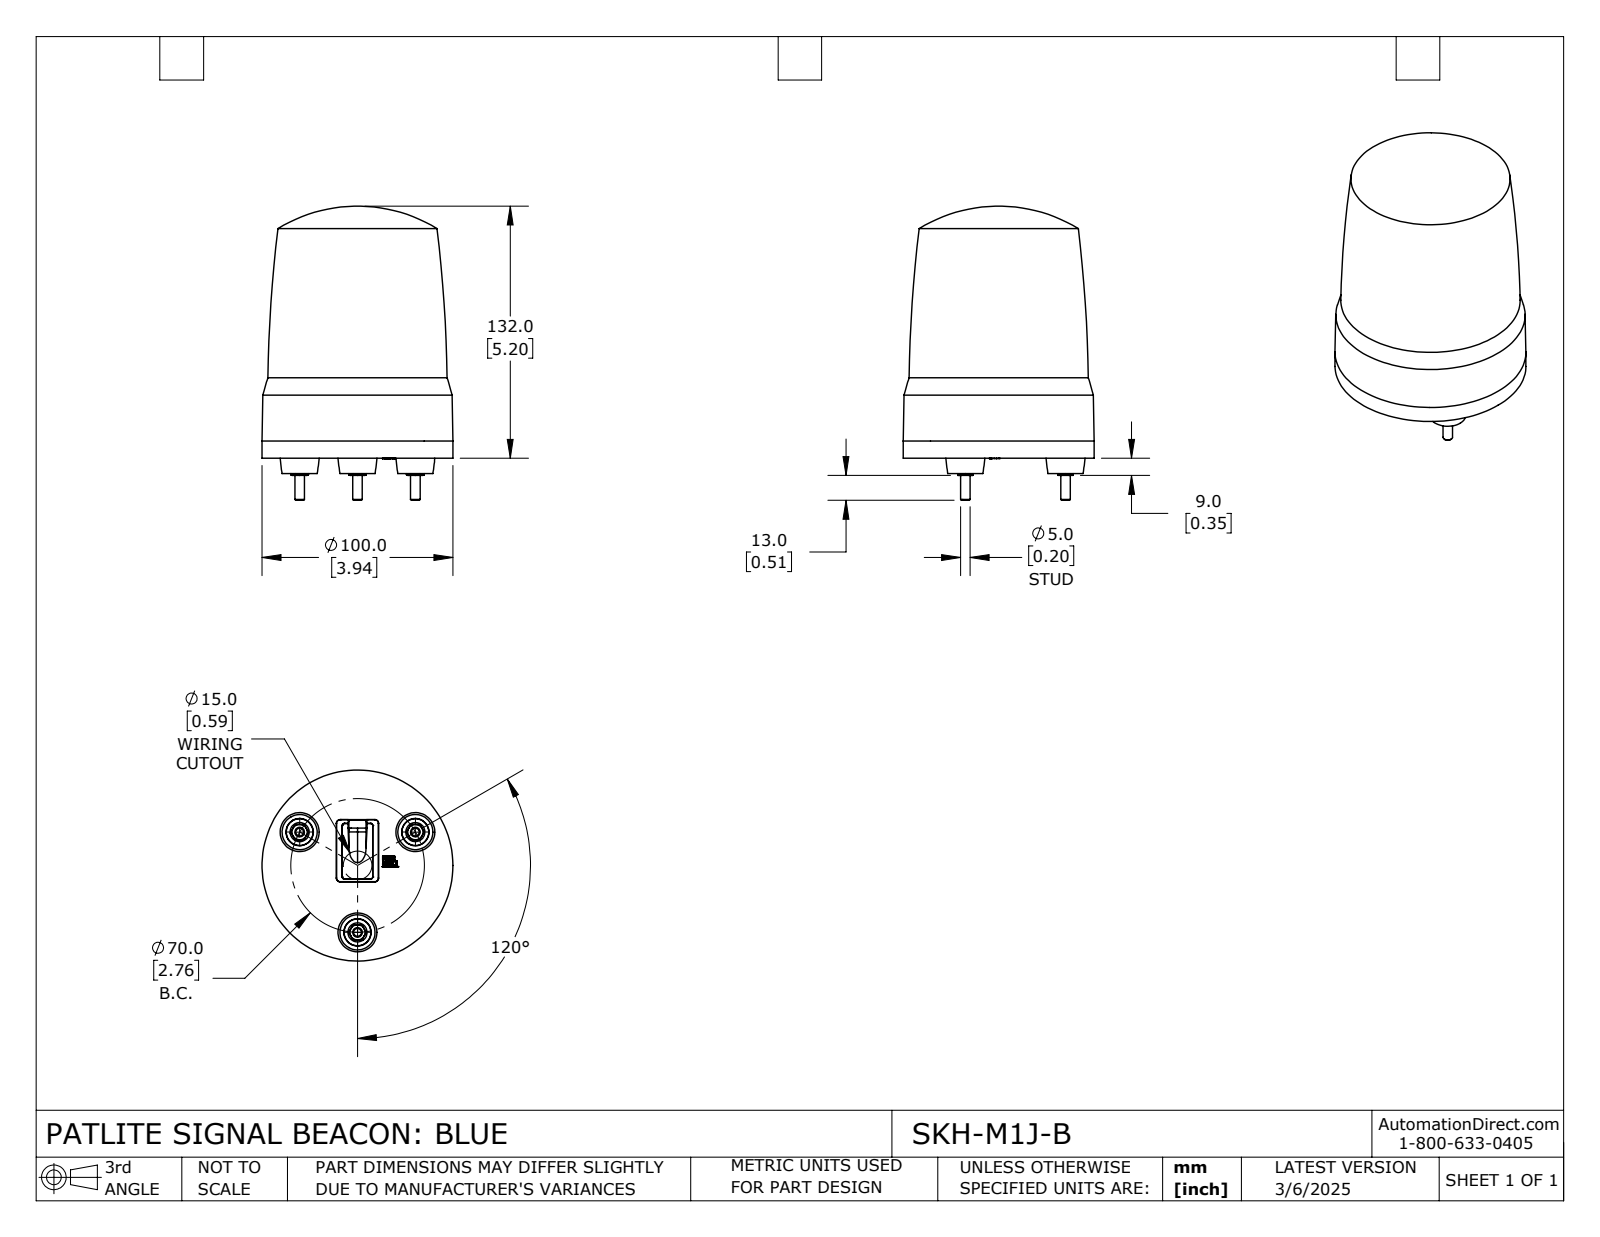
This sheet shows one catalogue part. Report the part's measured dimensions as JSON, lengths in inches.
{"part_name": "SKH-M1J-B", "step_written_by": "SolidWorks 2024 (CONFIG_CONTROL_DESIGN)", "units": "inches", "bodies": {"solids": 1, "faces": 327, "planar": 159, "cylindrical": 14, "other": 154}, "overall_size": [6.063, 3.937, 3.937], "volume_in3": 52.48, "surface_area_in2": 81.51, "round_bosses_or_shafts": [[0.394, 3], [0.197, 3], [3.937, 1]], "face_to_face_distances": [0.315, 0.033, 0.348, 0.063, 0.411, 0.096, 0.15, 0.165, 0.199, 0.262]}
